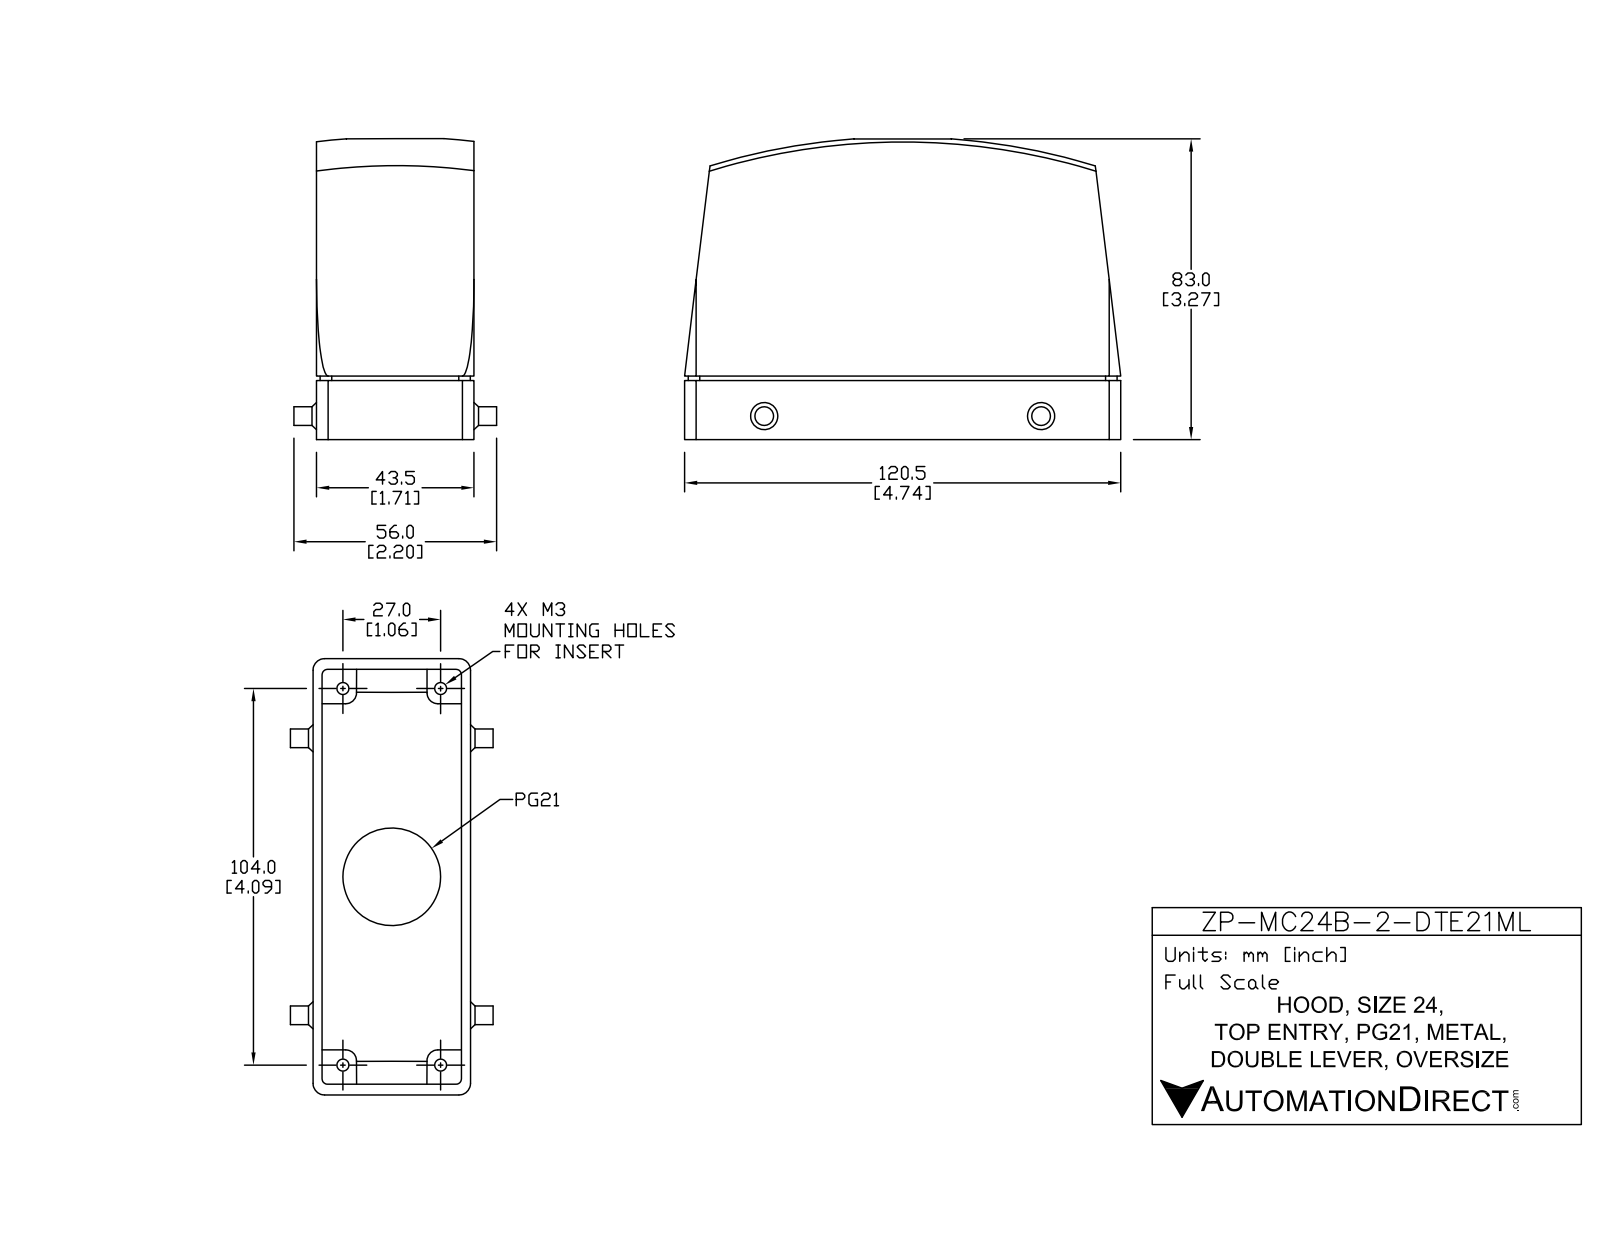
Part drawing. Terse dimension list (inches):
name: ZP-MC24B-2-DTE21ML
written by: SolidWorks 2011 (AUTOMOTIVE_DESIGN)
unit: in
bodies: 9 solids, 98 faces (58 planar, 30 cylindrical, 10 other)
size: 4.744 × 3.035 × 2.205
volume: 4.86 in³; area: 96.01 in²
holes: 4× ⌀0.138, 1× ⌀1.063
bosses: 2× ⌀0.204
rounds: 8× R0.126, 4× R0.059, 4× R0.118, 1× R0.028
face distances: 0.098, 1.614, 1.713, 1.516, 0.374, 4.137, 0.117, 0.491, 4.254, 4.628
hole spacings: 2.115, 1.063, 4.094, 4.23
